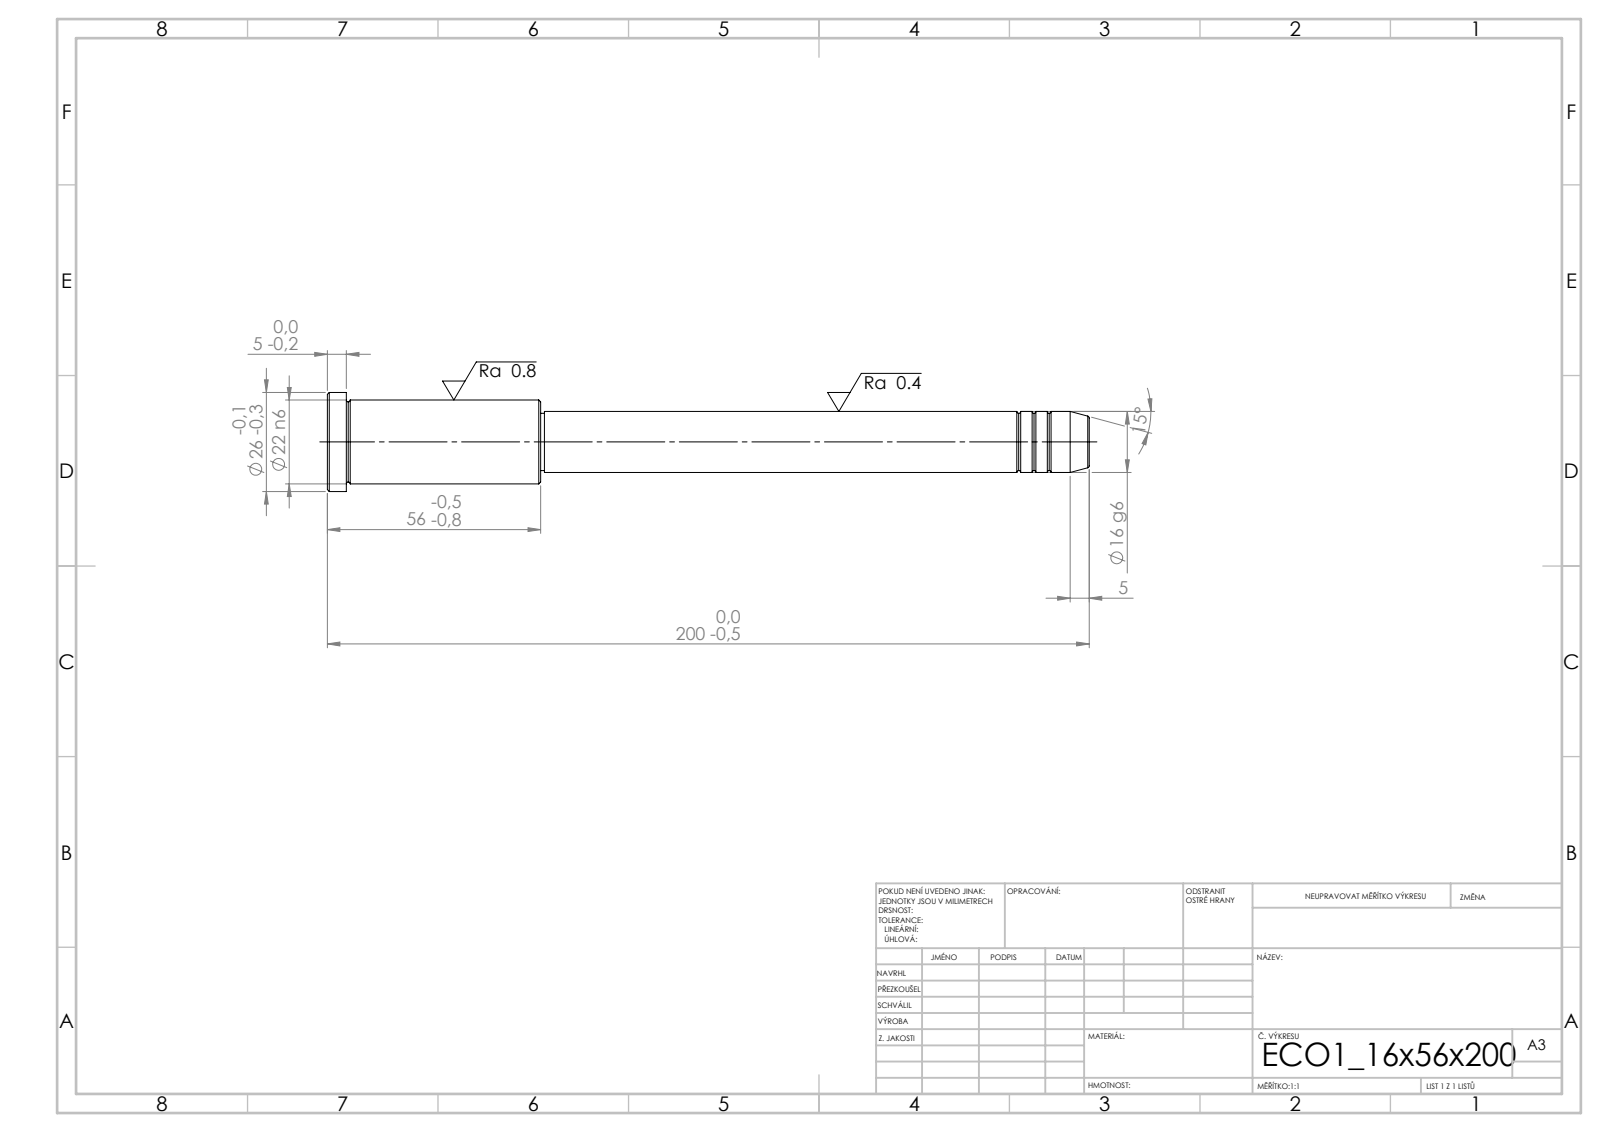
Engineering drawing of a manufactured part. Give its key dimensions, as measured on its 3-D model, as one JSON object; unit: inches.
{"step_written_by": "SolidWorks 2019 (CONFIG_CONTROL_DESIGN)", "units": "inches", "bodies": {"solids": 1, "faces": 43, "planar": 5, "cylindrical": 14, "other": 24}, "overall_size": [7.874, 1.024, 1.024], "volume_in3": 3.094, "surface_area_in2": 19.02, "round_bosses_or_shafts": [[1.024, 1], [0.866, 1], [0.63, 1], [0.591, 1]], "face_to_face_distances": [2.205, 2.008, 0.197, 5.669, 7.677, 7.874, 5.63, 0.039, 2.047, 2.244]}
